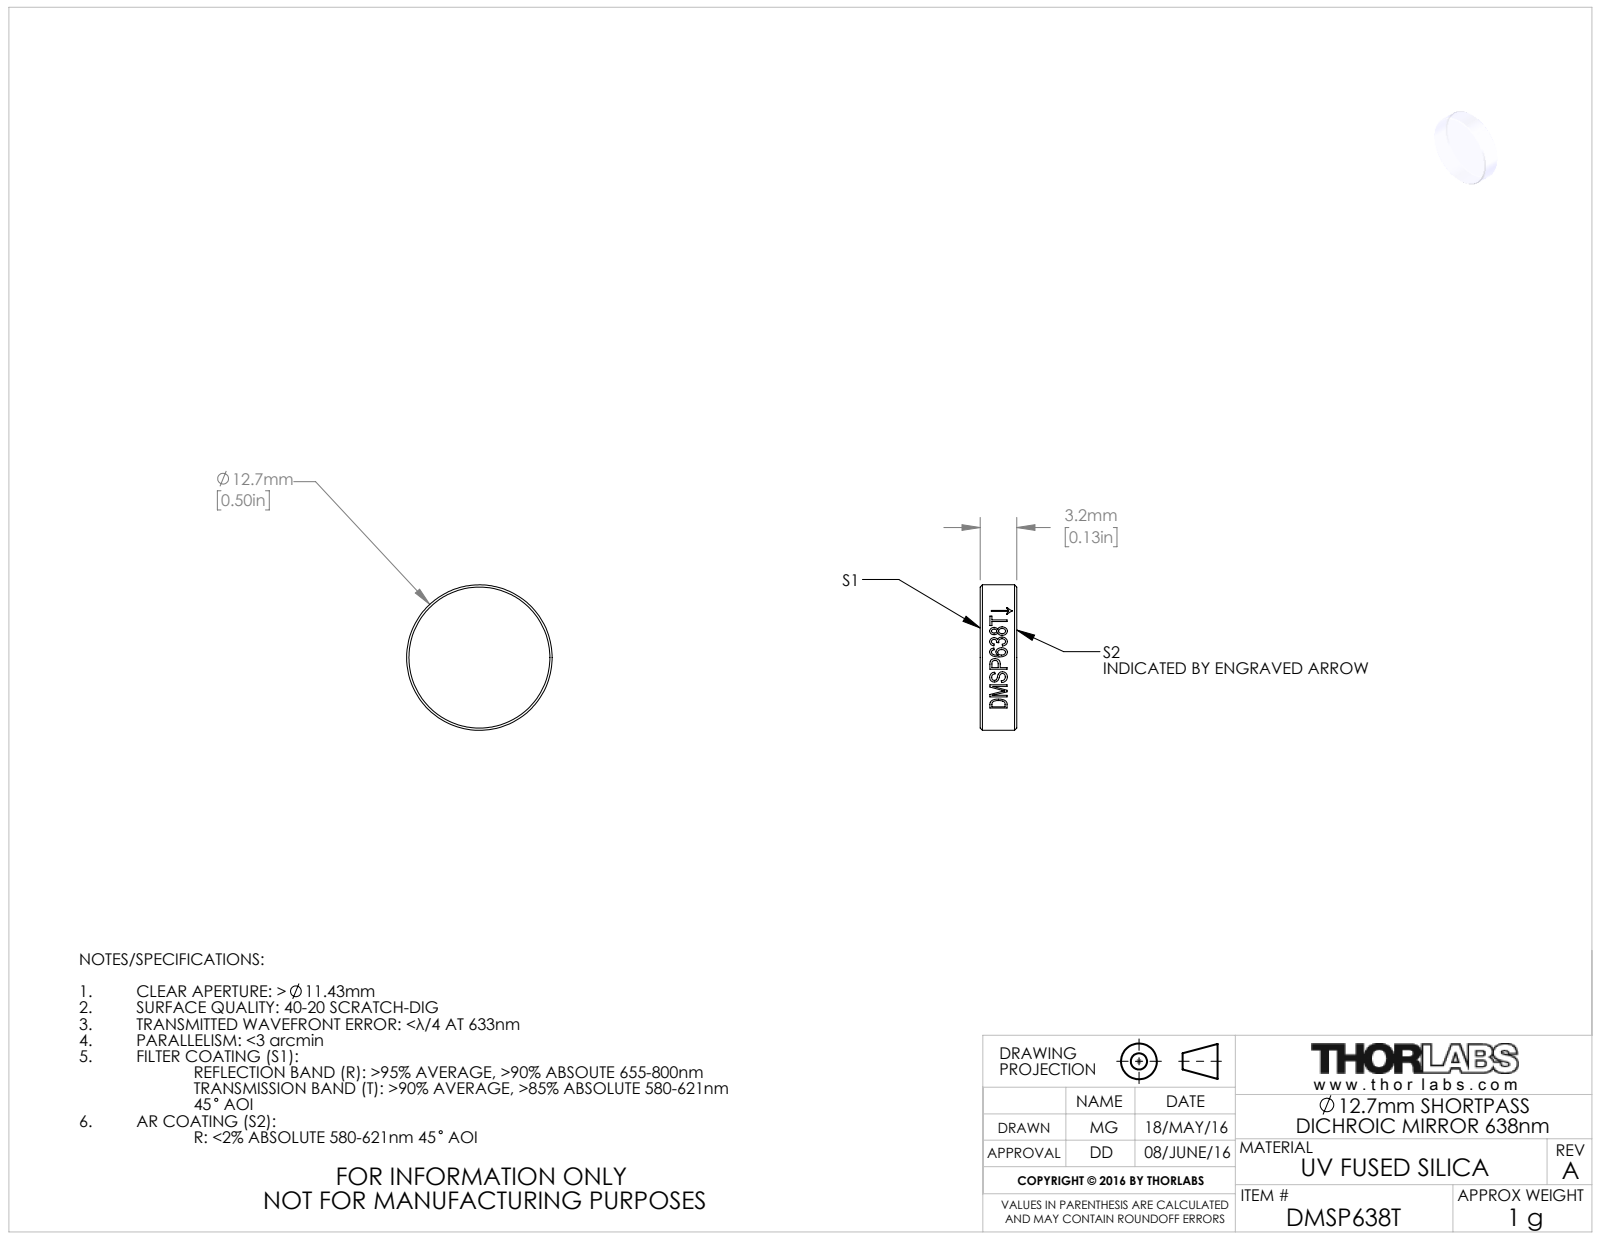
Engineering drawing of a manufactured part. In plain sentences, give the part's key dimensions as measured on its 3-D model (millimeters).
The part is named "TTN045286-E0W". Its 3-D file was written by "SolidWorks 2016 (CONFIG_CONTROL_DESIGN)". It is 1 solid with 22 faces: 2 planar, 16 cylindrical and 4 other. Overall it measures 12.7 by 12.7 by 3.2 millimeters. Its volume is 404 cubic millimeters and its surface area 372 square millimeters. Round bosses or shafts: 1 of diameter 12.7. The main face-to-face distances are 3.2.
